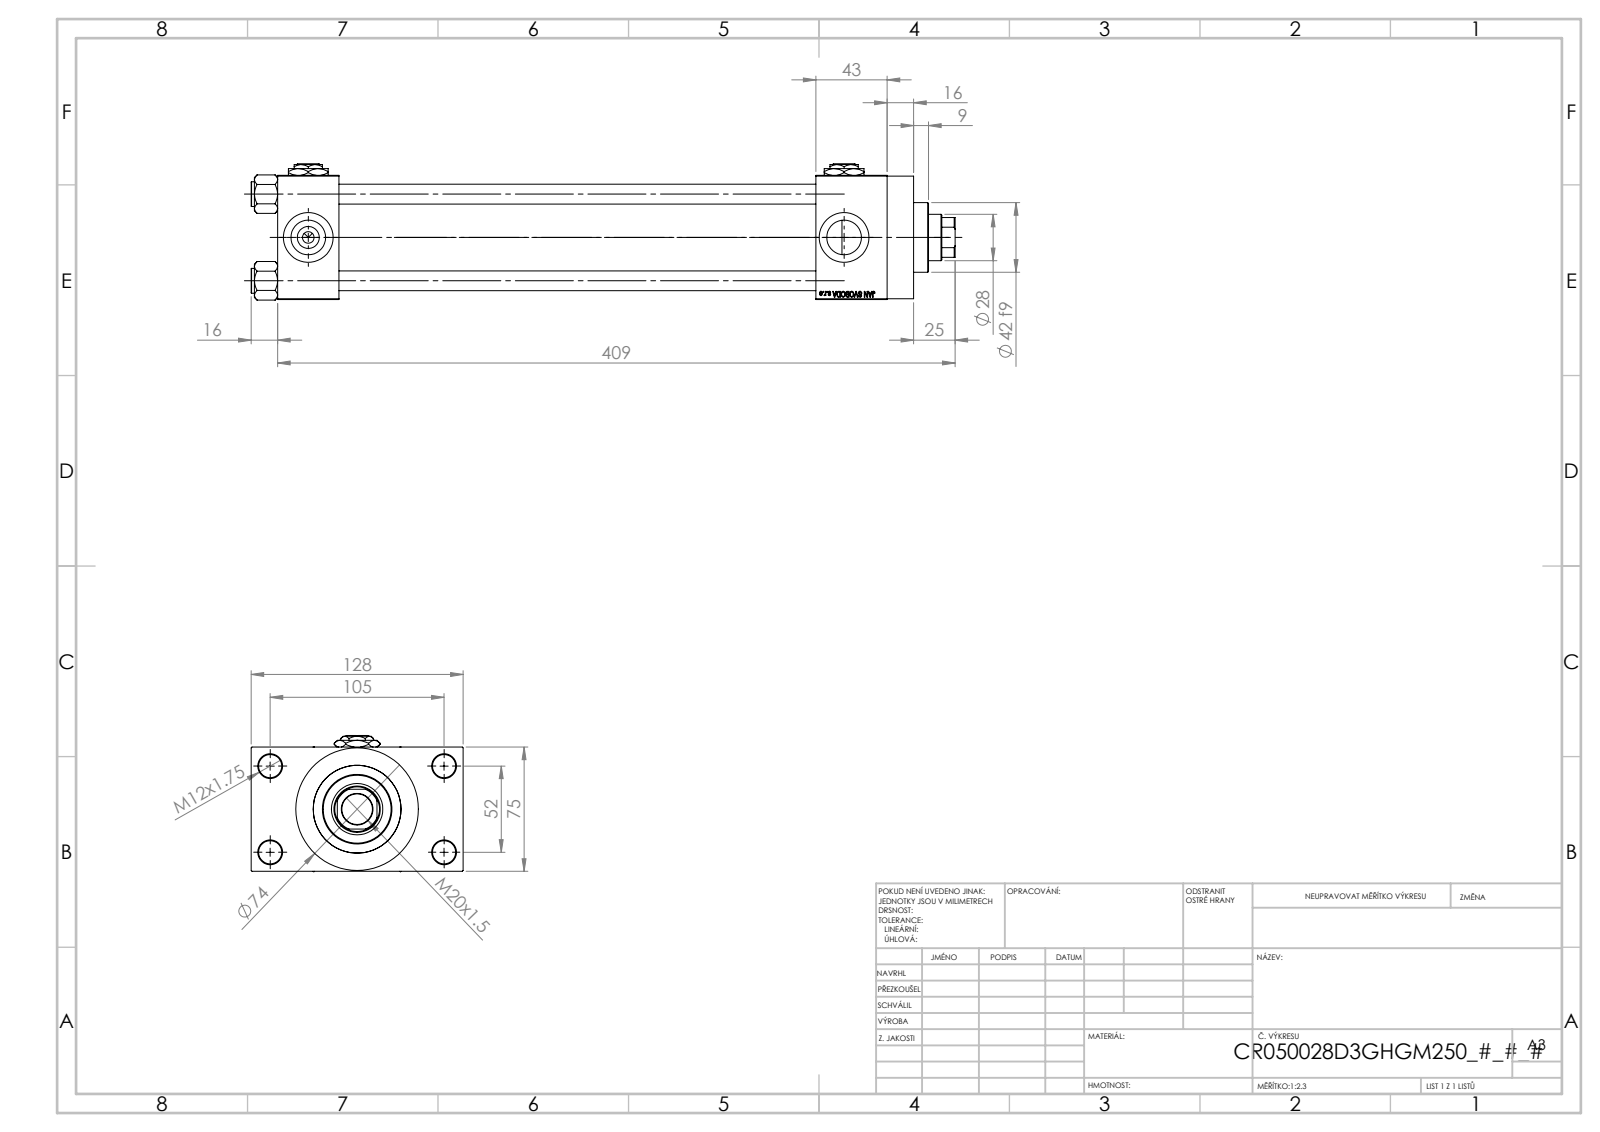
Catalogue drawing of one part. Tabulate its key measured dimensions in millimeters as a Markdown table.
| quantity | value |
| --- | --- |
| part name | V215CR_VCP_D; V215CR_D_TYCINKA; NUT_M5_D; V215_VC_A (+2 more) |
| STEP written by | SolidWorks 2019 (CONFIG_CONTROL_DESIGN) |
| units | millimeters |
| bodies | 13 solids, 1204 faces (545 planar, 99 cylindrical, 560 other) |
| overall size | 425 × 128 × 82.27 |
| volume | 1 162 000 mm³ |
| surface area | 306 349 mm² |
| round holes (diameter × count) | 12 × 4, 14 × 4, 20.96 × 4, 30 × 4, 7 × 3, 18.5 × 1, 28 × 1, 31 × 1, 41 × 1, 50 × 1, 53 × 1 |
| round bosses / shafts (diameter × count) | 15 × 4, 74 × 1, 56 × 1, 42 × 1 |
| partial cylindrical surfaces (radius × count) | 13.5 × 1 |
| main face-to-face distances | 75, 288, 37, 325, 26.5, 368, 331, 43, 101.5, 16 |
| hole center spacings | 26.35, 36.98, 52.3, 58.43, 58.59, 78.65, 94.37, 52 |
